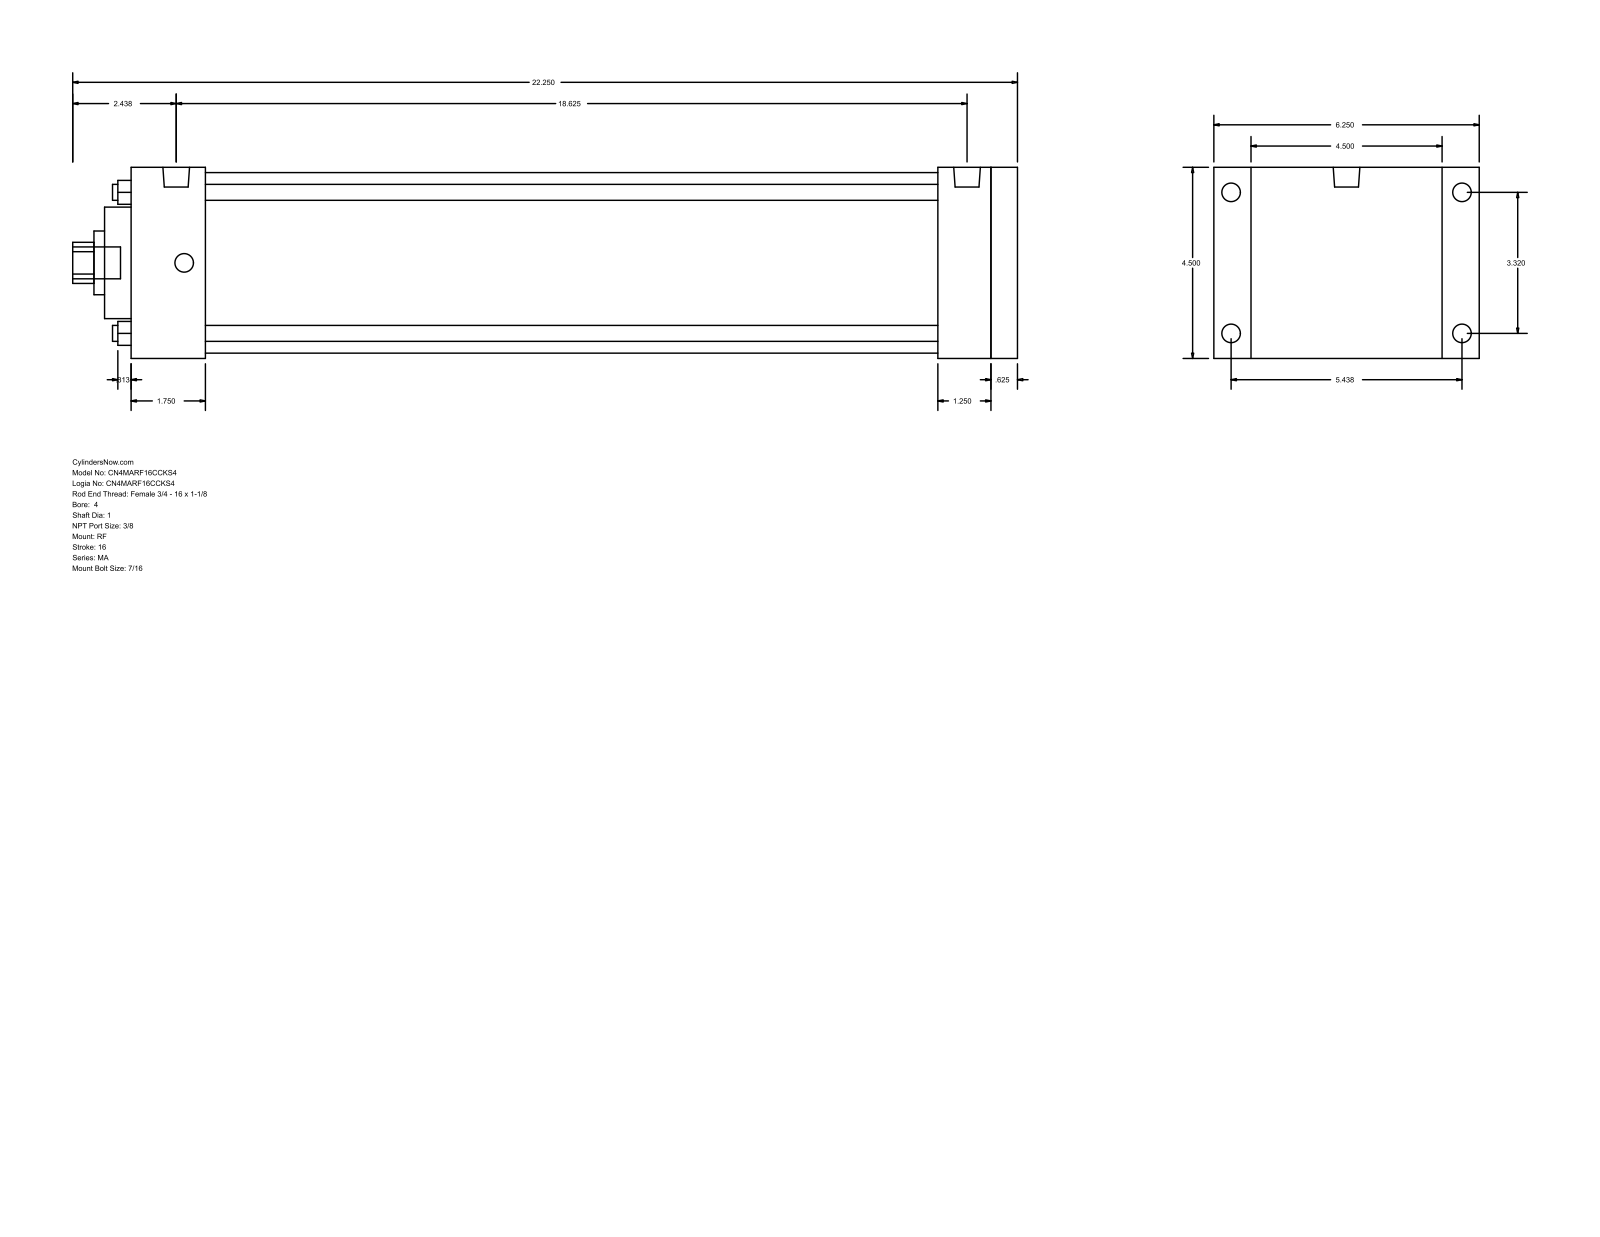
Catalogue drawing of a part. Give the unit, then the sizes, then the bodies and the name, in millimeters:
Units: millimetres
Overall size (bounding box): 565.15 × 158.75 × 114.3
Round holes (diameter × count): ⌀9.53 ×4, ⌀25.4 ×1, ⌀38.1 ×1, ⌀66.67 ×1, ⌀107.95 ×1
Round bosses / shafts (diameter × count): ⌀11.11 ×8, ⌀15.93 ×2, ⌀19.05 ×1
Partial cylindrical surfaces — rounded edges, fillets, slot ends (radius × count): R12.29 ×1
Main face-to-face distances: 114.3, 530.23, 514.35, 15.88, 22.23, 136.53, 482.6, 31.75, 47.63, 44.46
Hole centre spacings: 59.62, 84.32, 119.25
Bodies: 0 solids, 94 faces (65 planar, 29 cylindrical, 0 other)
Part name (STEP PRODUCT): MA_RF__0400_1
STEP written by: GSSL Pune (CONFIG_CONTROL_DESIGN)
